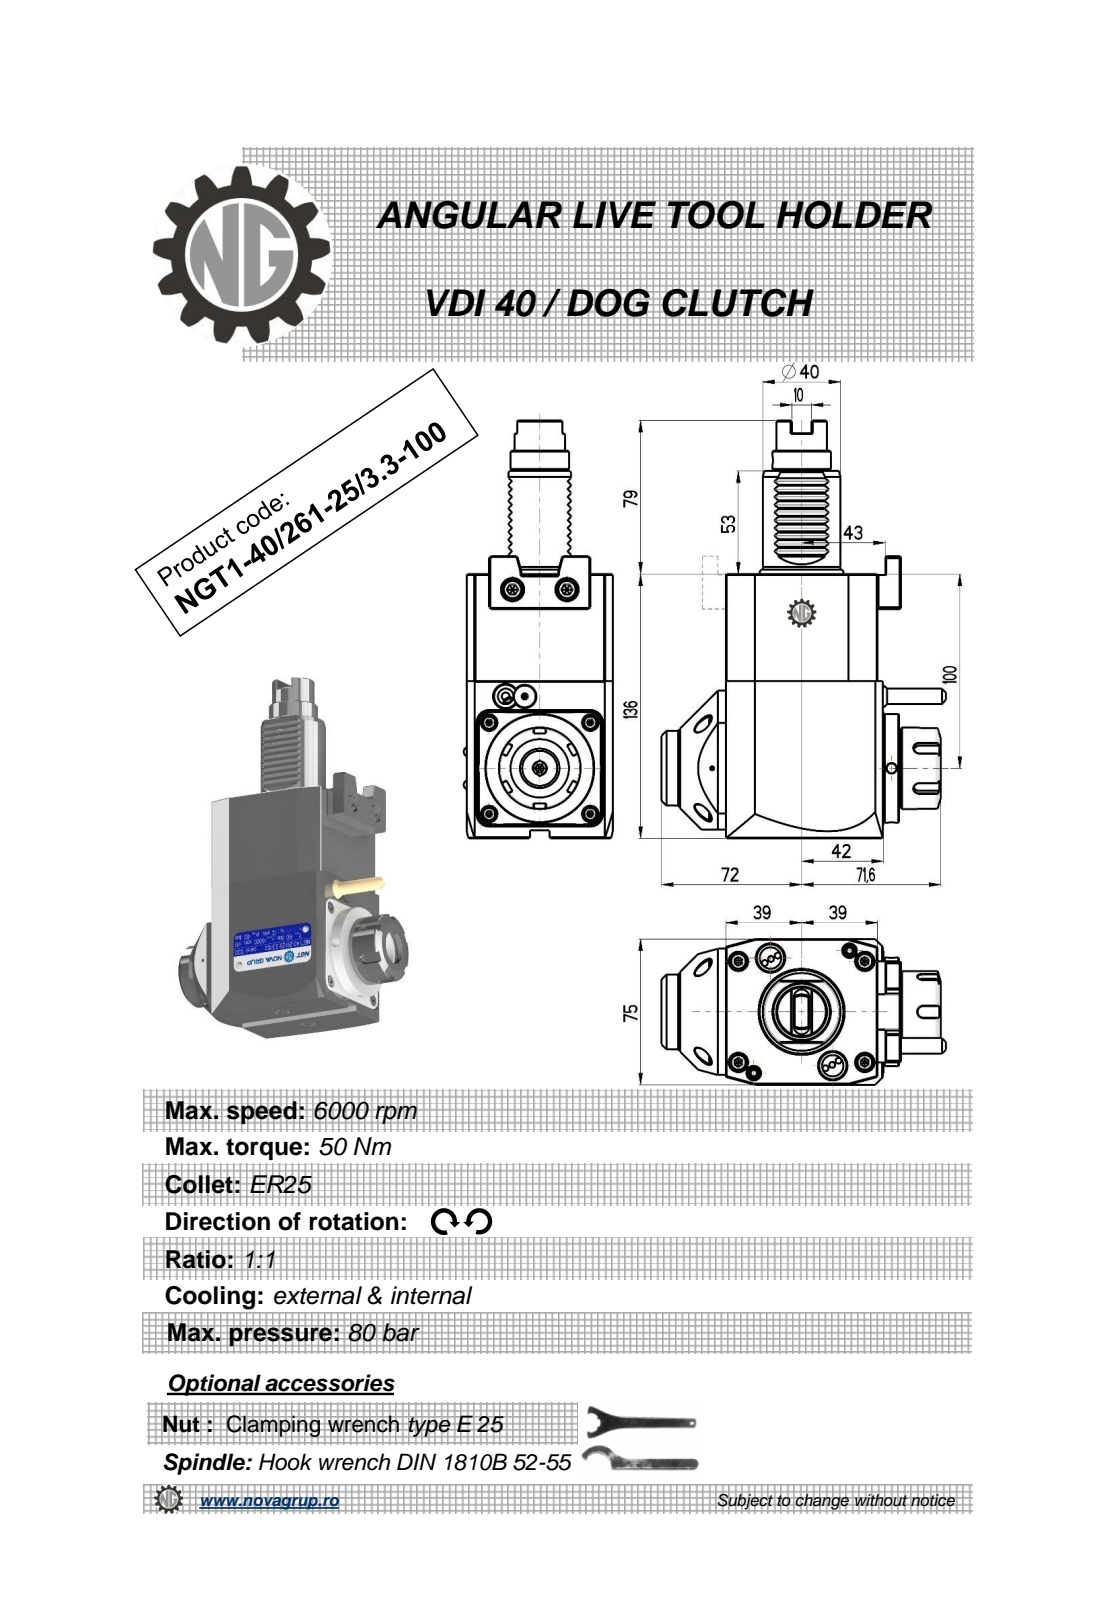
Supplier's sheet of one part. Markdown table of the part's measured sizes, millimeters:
| quantity | value |
| --- | --- |
| part name | NGT1_40_261_25_3_3_100 |
| STEP written by | PRO/ENGINEER BY PARAMETRIC TECHNOLOGY CORPORATION, 2010280 (CONFIG_CONTROL_DESIGN) |
| units | millimeters |
| bodies | 1 solid, 452 faces (234 planar, 85 cylindrical, 133 other) |
| overall size | 215 × 146.14 × 75 |
| volume | 1 011 000 mm³ |
| surface area | 78 210 mm² |
| round holes (diameter × count) | 5 × 3, 3 × 1, 4.2 × 1, 20.3 × 1 |
| round bosses / shafts (diameter × count) | 56 × 1, 43 × 1, 42 × 1, 40 × 1, 38.5 × 1, 33 × 1, 30 × 1, 26 × 1 |
| partial cylindrical surfaces (radius × count) | 0.3 × 20, 0.22 × 6, 0.26 × 6, 3 × 5, 0.5 × 2, 1 × 2, 12.5 × 1, 40 × 1 |
| main face-to-face distances | 75, 136, 78, 81, 3, 0.5, 11, 8, 1, 8.2 |
| hole center spacings | 40.93, 122.75, 158.5 |
